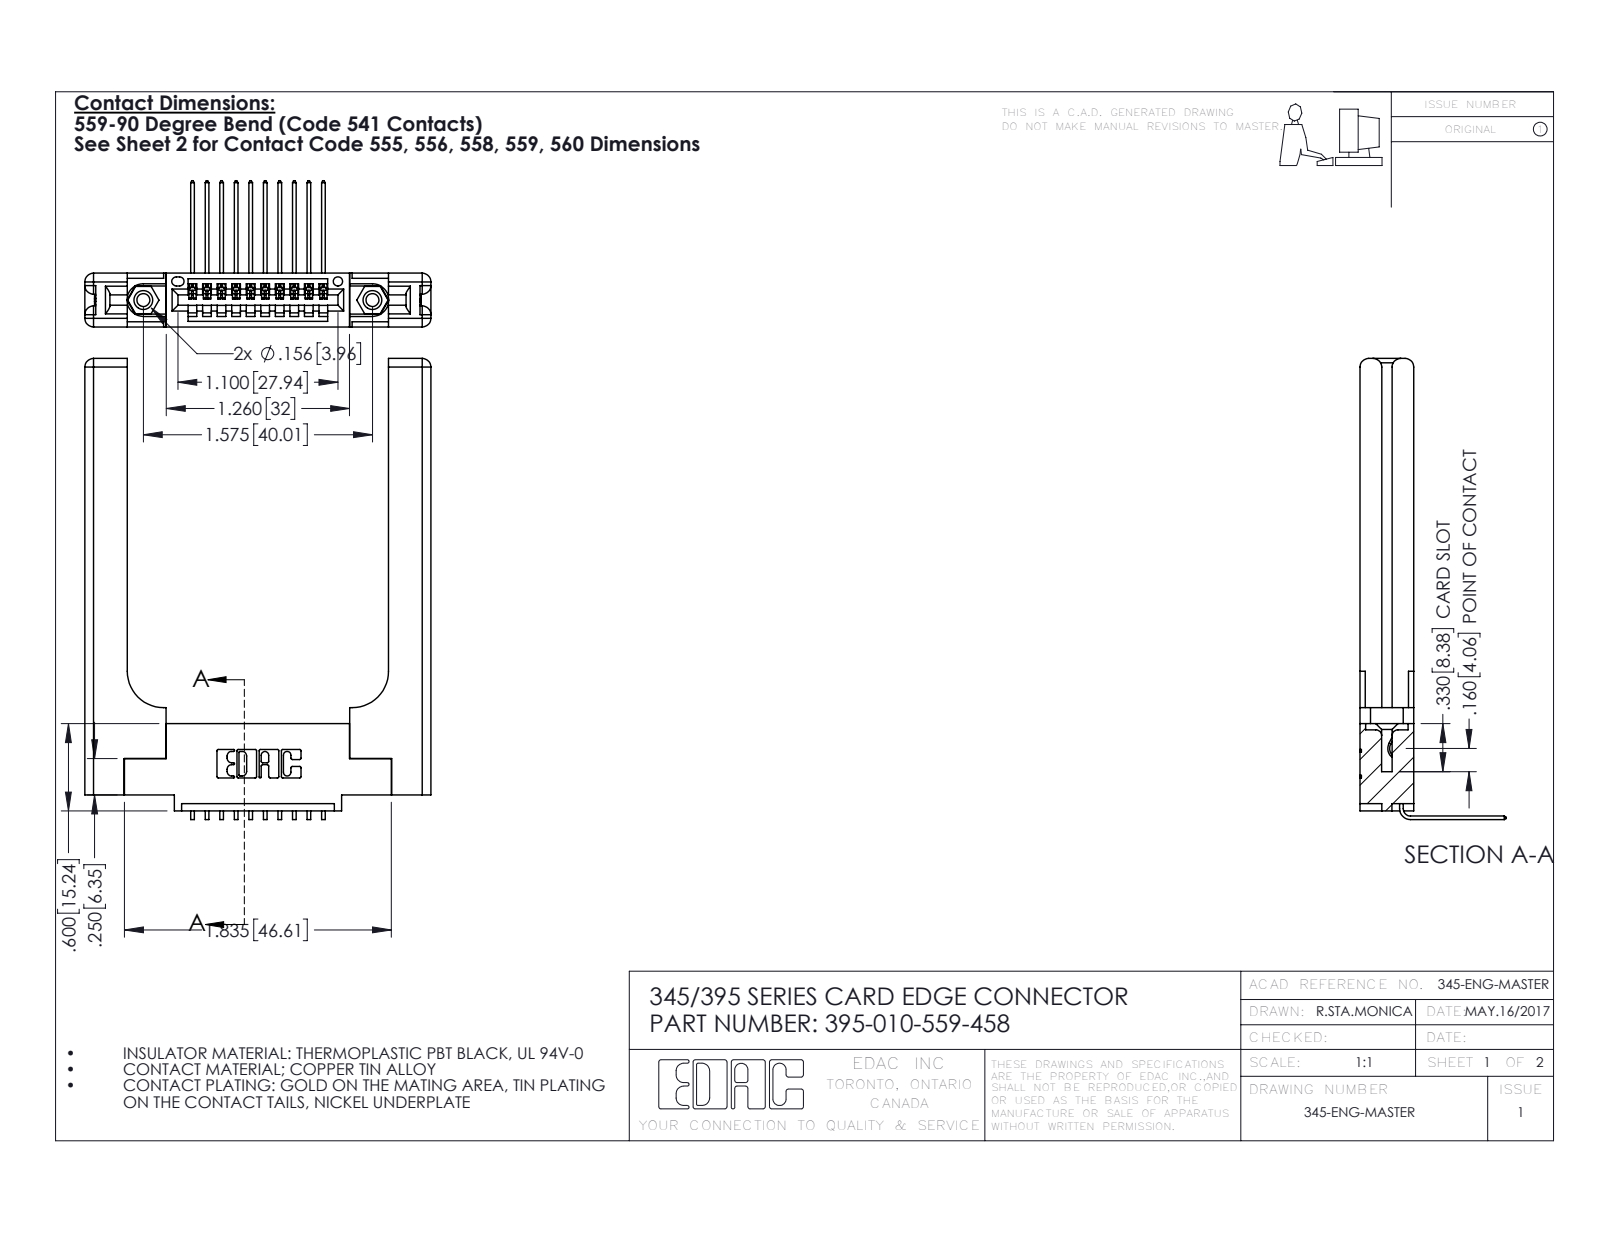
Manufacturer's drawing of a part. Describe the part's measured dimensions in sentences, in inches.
The part is named "395-010-559-458; 345 Part_0.110 Offset - 0.156 Dia-TH; 345-250-001_345-250-001-102; 345-292-001_558 559 Tail - 1 (+1 more)". Its 3-D file was written by "SolidWorks 2016 (CONFIG_CONTROL_DESIGN)". It is 15 solids with 986 faces: 652 planar, 274 cylindrical and 60 other. Overall it measures 3.169 by 2.379 by 1.005 inches. Its volume is 0.851 cubic inches and its surface area 19.18 square inches. Round holes: 2 of diameter 0.089, 2 of diameter 0.125, 2 of diameter 0.156, 1 of diameter 0.064. Round bosses or shafts: 2 of diameter 0.155. Partial cylindrical surfaces (rounded edges, fillets, slot ends): 22 of radius 0.01, 20 of radius 0.006, 16 of radius 0.06, 6 of radius 0.007, 6 of radius 0.031, 3 of radius 0.026, 2 of radius 0.03, 2 of radius 0.031. The main face-to-face distances are 0.37, 0.15, 0.072, 0.22, 0.148, 0.077, 0.298, 1.796, 0.071, 0.292. The hole center spacings are 0.27, 1.344, 1.575.
